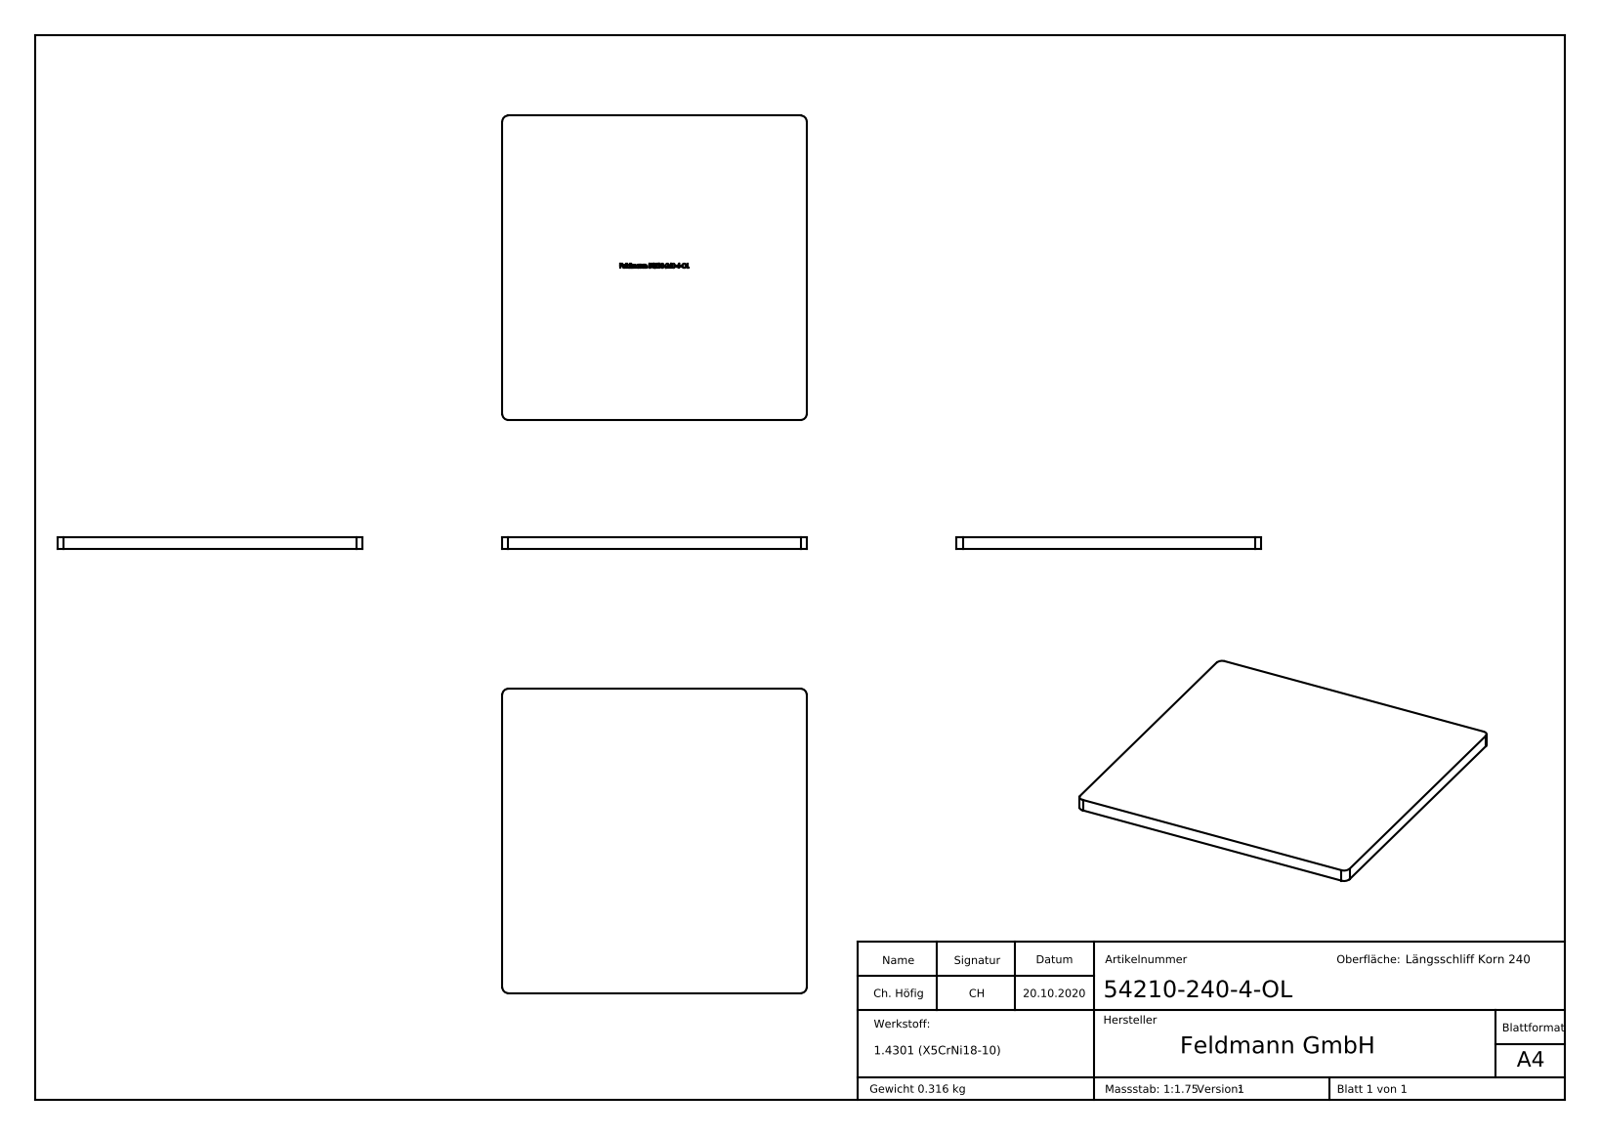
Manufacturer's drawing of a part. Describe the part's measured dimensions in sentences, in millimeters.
The part is named "54210-240-4-OL". Its 3-D file was written by "SolidWorks 2018 (CONFIG_CONTROL_DESIGN)". It is 1 solid with 270 faces: 172 planar, 4 cylindrical and 94 other. Overall it measures 100 by 100 by 4 millimeters. Its volume is 39 986 cubic millimeters and its surface area 21 591 square millimeters. Partial cylindrical surfaces (rounded edges, fillets, slot ends): 4 of radius 2. The main face-to-face distances are 4, 100, 3.9, 50, 0.44, 50.44, 49.56, 0.88, 0.58, 21.99.
